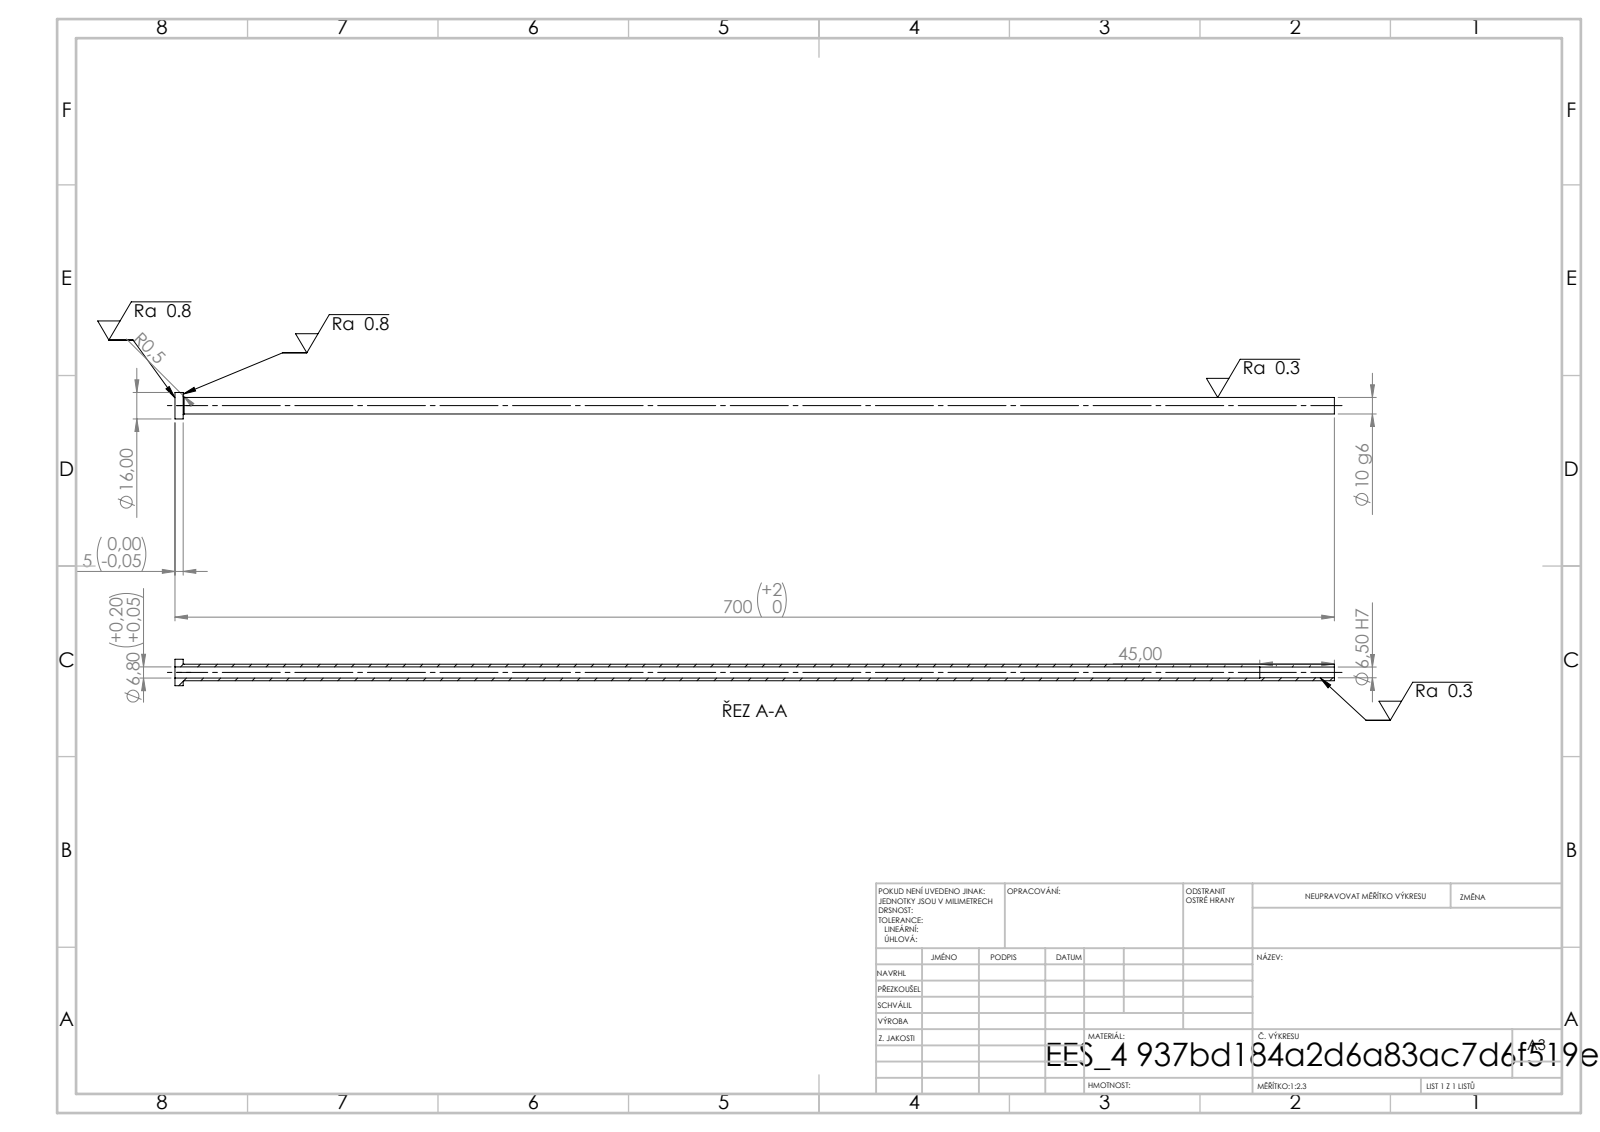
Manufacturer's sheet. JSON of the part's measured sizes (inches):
{"step_written_by": "SolidWorks 2019 (CONFIG_CONTROL_DESIGN)", "units": "inches", "bodies": {"solids": 1, "faces": 14, "planar": 4, "cylindrical": 8, "other": 2}, "overall_size": [27.559, 0.63, 0.63], "volume_in3": 1.85, "surface_area_in2": 57.86, "round_holes": [[0.256, 1], [0.268, 1]], "round_bosses_or_shafts": [[0.63, 1], [0.394, 1]], "face_to_face_distances": [0.197, 27.559, 27.362, 25.787, 25.591, 1.772]}
